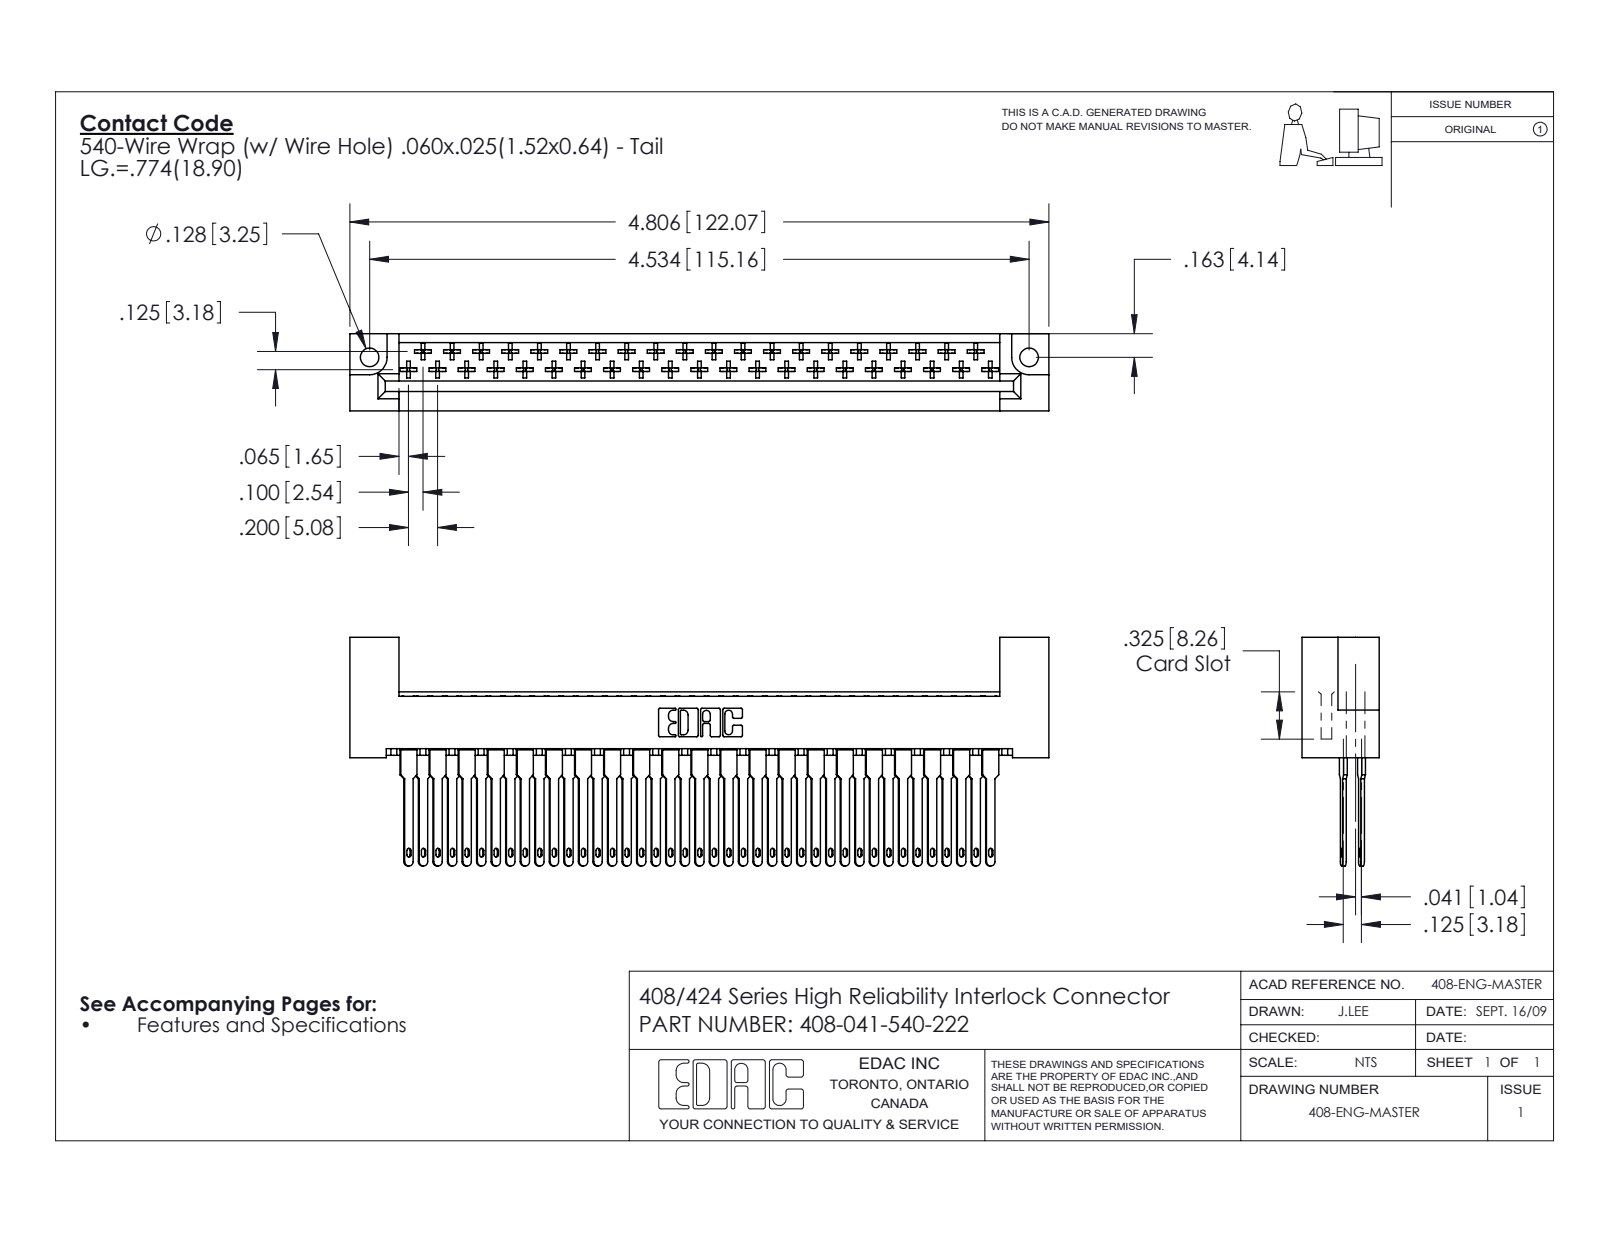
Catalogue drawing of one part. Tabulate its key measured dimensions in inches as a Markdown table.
| quantity | value |
| --- | --- |
| part name | 408 Part_041 - 2; 408-290-001_408-290-140; 408-041-540-222 |
| STEP written by | SolidWorks 2016 (CONFIG_CONTROL_DESIGN) |
| units | inches |
| bodies | 42 solids, 2476 faces (1811 planar, 501 cylindrical, 164 other) |
| overall size | 4.806 × 1.572 × 0.531 |
| volume | 0.962 in³ |
| surface area | 32.09 in² |
| round holes (diameter × count) | 0.128 × 2 |
| partial cylindrical surfaces (radius × count) | 0.01 × 246, 0.015 × 82, 0.02 × 43, 0.03 × 41, 0.01 × 22, 0.007 × 6, 0.031 × 6, 0.026 × 3 |
| main face-to-face distances | 0.531, 0.125, 0.1, 0.025, 0.025, 0.361, 0.235, 0.259, 0.217, 0.272 |
| hole center spacings | 4.534 |
